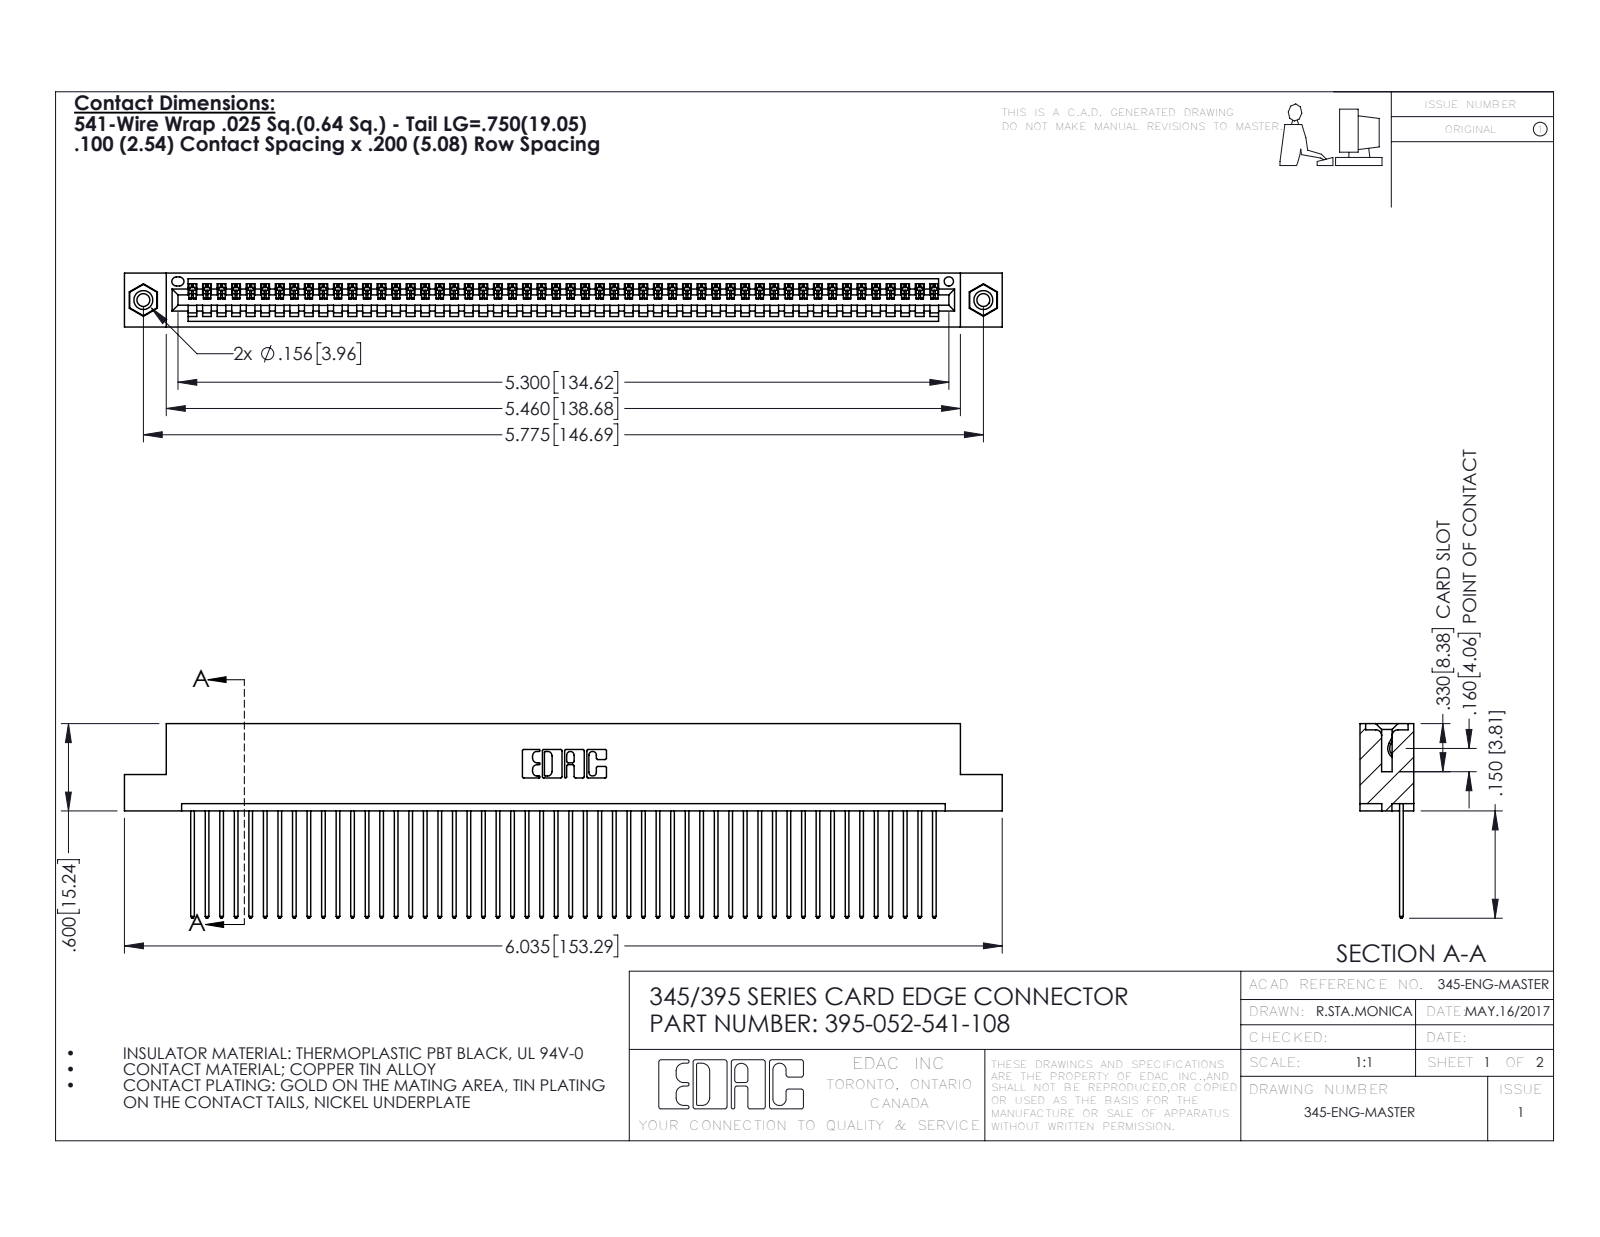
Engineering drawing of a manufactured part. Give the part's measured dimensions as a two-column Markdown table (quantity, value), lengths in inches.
| quantity | value |
| --- | --- |
| part name | 345-250-001_345-250-003-102; 345 Part_Flush Mounting Lugs - 0.156 Dia-TI; 345-292-001_345-293-141; 395-052-541-108 |
| STEP written by | SolidWorks 2016 (CONFIG_CONTROL_DESIGN) |
| units | inches |
| bodies | 55 solids, 3202 faces (2192 planar, 994 cylindrical, 16 other) |
| overall size | 6.035 × 1.337 × 0.37 |
| volume | 0.904 in³ |
| surface area | 32.3 in² |
| round holes (diameter × count) | 0.089 × 2, 0.125 × 2, 0.156 × 2, 0.064 × 1 |
| round bosses / shafts (diameter × count) | 0.155 × 2 |
| partial cylindrical surfaces (radius × count) | 0.006 × 104, 0.01 × 104, 0.01 × 22, 0.007 × 6, 0.031 × 6, 0.026 × 3, 0.031 × 2, 0.04 × 2 |
| main face-to-face distances | 0.072, 0.298, 0.098, 0.272, 0.025, 0.37, 0.2, 0.225, 0.149, 0.072 |
| hole center spacings | 0.27, 5.539, 5.775 |
